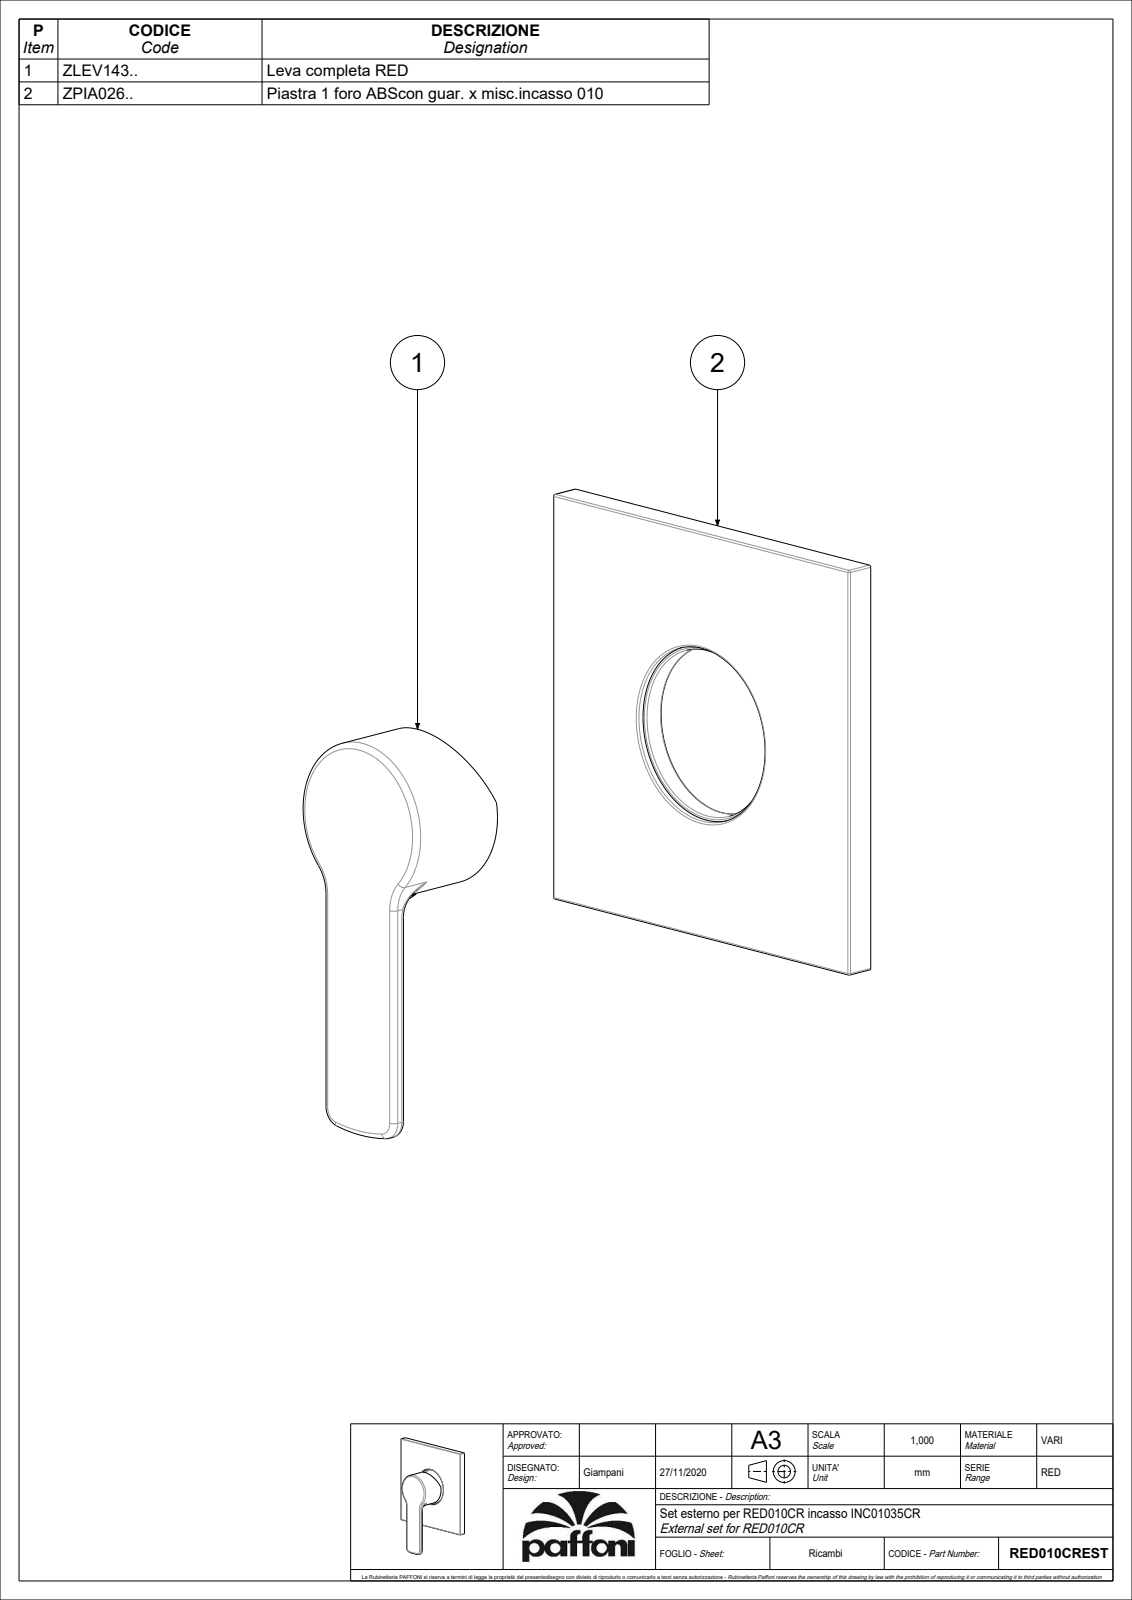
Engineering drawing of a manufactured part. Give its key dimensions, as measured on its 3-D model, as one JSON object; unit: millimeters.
{"part_name": "RED010CREST", "step_written_by": "CREO PARAMETRIC BY PTC INC, 2020044 (CONFIG_CONTROL_DESIGN)", "units": "millimeters", "bodies": {"solids": 2, "faces": 316, "planar": 90, "cylindrical": 115, "other": 111}, "overall_size": [140, 110, 40.23], "volume_mm3": 83341, "surface_area_mm2": 48411, "round_holes": [[3, 1], [3.3, 1], [4.5, 1], [45, 1], [47, 1], [49, 1]], "round_bosses_or_shafts": [[51, 1], [43, 1], [7.6, 1], [5.5, 1], [5, 1]], "partial_cylinders_radius": [[0.5, 55], [1, 4], [1.5, 4], [2, 4], [5, 2], [10, 2], [50, 1]], "face_to_face_distances": [7, 2, 5, 108, 2.5, 34.5, 107.5, 0.5, 105.5, 29.5]}
